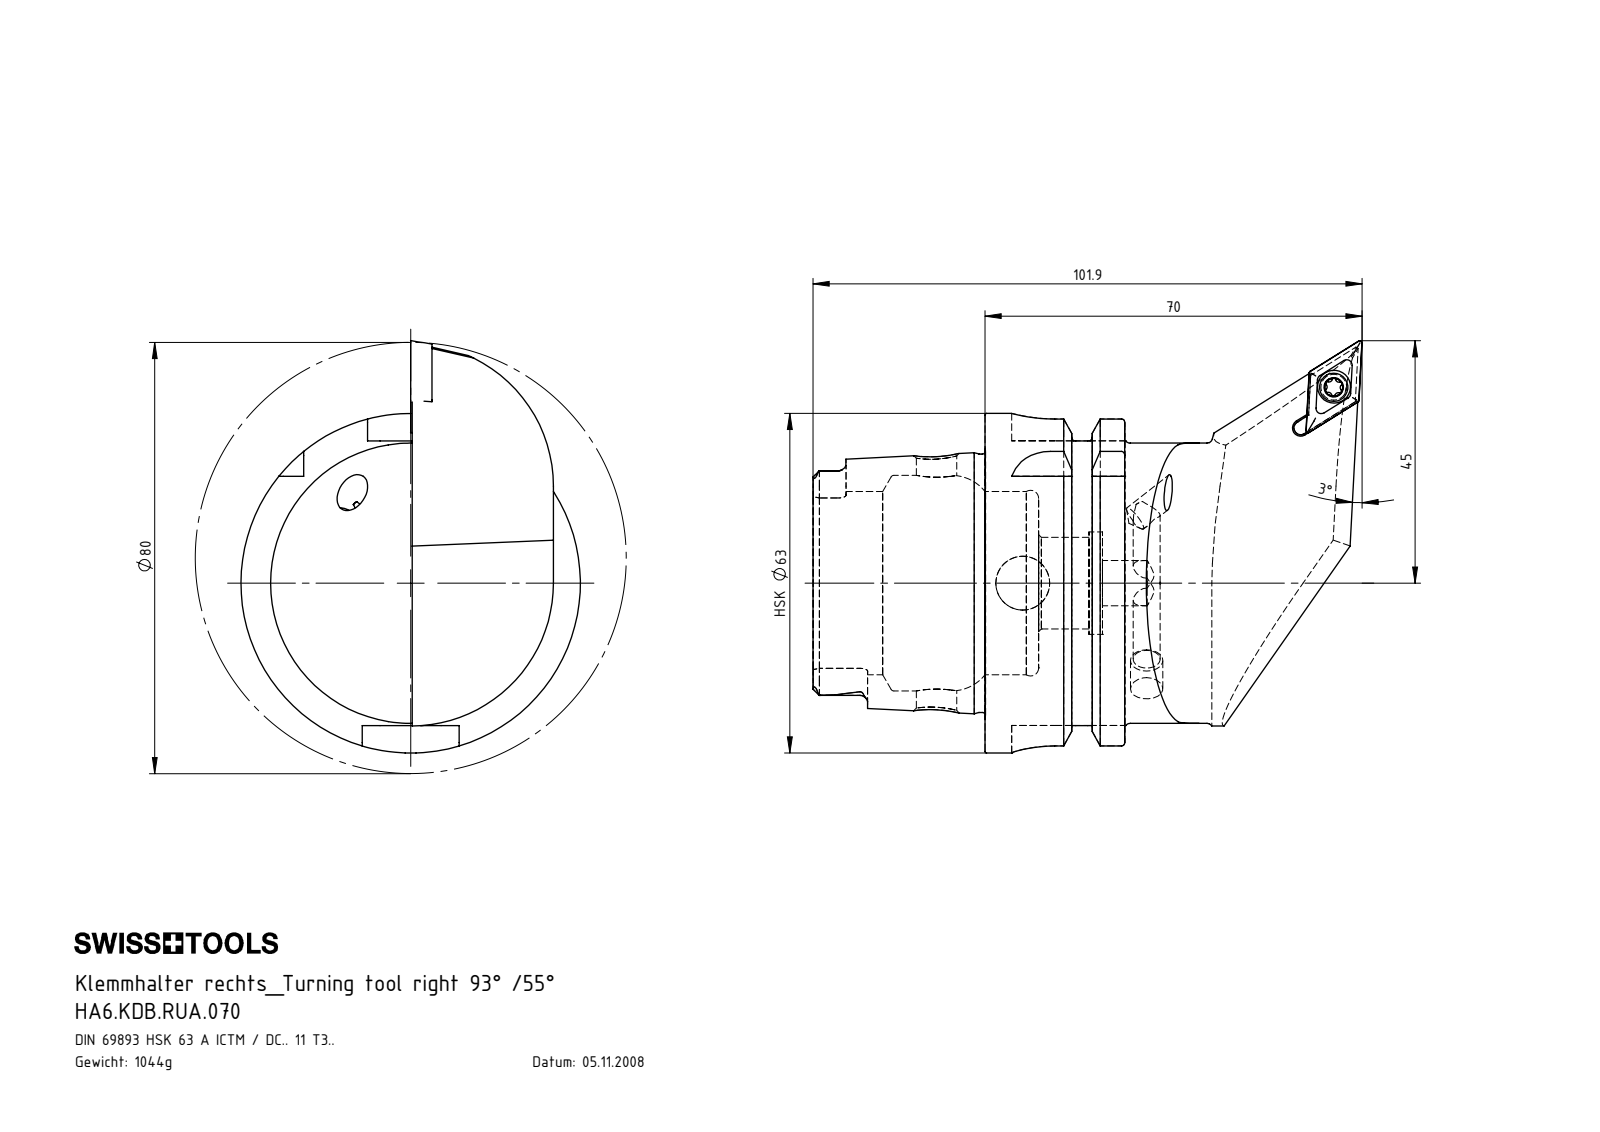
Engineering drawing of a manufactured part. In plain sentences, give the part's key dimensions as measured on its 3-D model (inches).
The part is named "KVT_MB_600_050; HA6.KDB.RUA.070; WCB-ER2.001.009_A; HA6-KDB.RUA.070_C (+1 more)". Its 3-D file was written by "SolidWorks 2017 (AUTOMOTIVE_DESIGN)". It is 5 solids with 311 faces: 80 planar, 88 cylindrical and 143 other. Overall it measures 4.012 by 3.012 by 2.48 inches. Its volume is 8.098 cubic inches and its surface area 46.04 square inches. Round holes: 1 of diameter 0.13, 1 of diameter 0.157, 1 of diameter 0.173, 1 of diameter 0.197, 1 of diameter 0.236, 1 of diameter 0.24, 1 of diameter 0.295, 1 of diameter 0.331, 1 of diameter 0.394, 1 of diameter 0.669, 1 of diameter 0.748, 1 of diameter 1.339. Round bosses or shafts: 1 of diameter 2.48, 1 of diameter 2.163, 1 of diameter 2.047, 1 of diameter 1.887, 1 of diameter 0.207, 1 of diameter 0.197, 1 of diameter 0.157. Partial cylindrical surfaces (rounded edges, fillets, slot ends): 6 of radius 0.013, 6 of radius 0.023, 6 of radius 0.055, 4 of radius 0.315, 2 of radius 0.111, 2 of radius 0.113, 2 of radius 1.043, 1 of radius 0.049. The main face-to-face distances are 1.022, 0.63, 0.392, 1.031, 1.256, 1.648, 2.278, 2.079, 0.858, 0.467. The hole center spacings are 2.686, 2.691.
